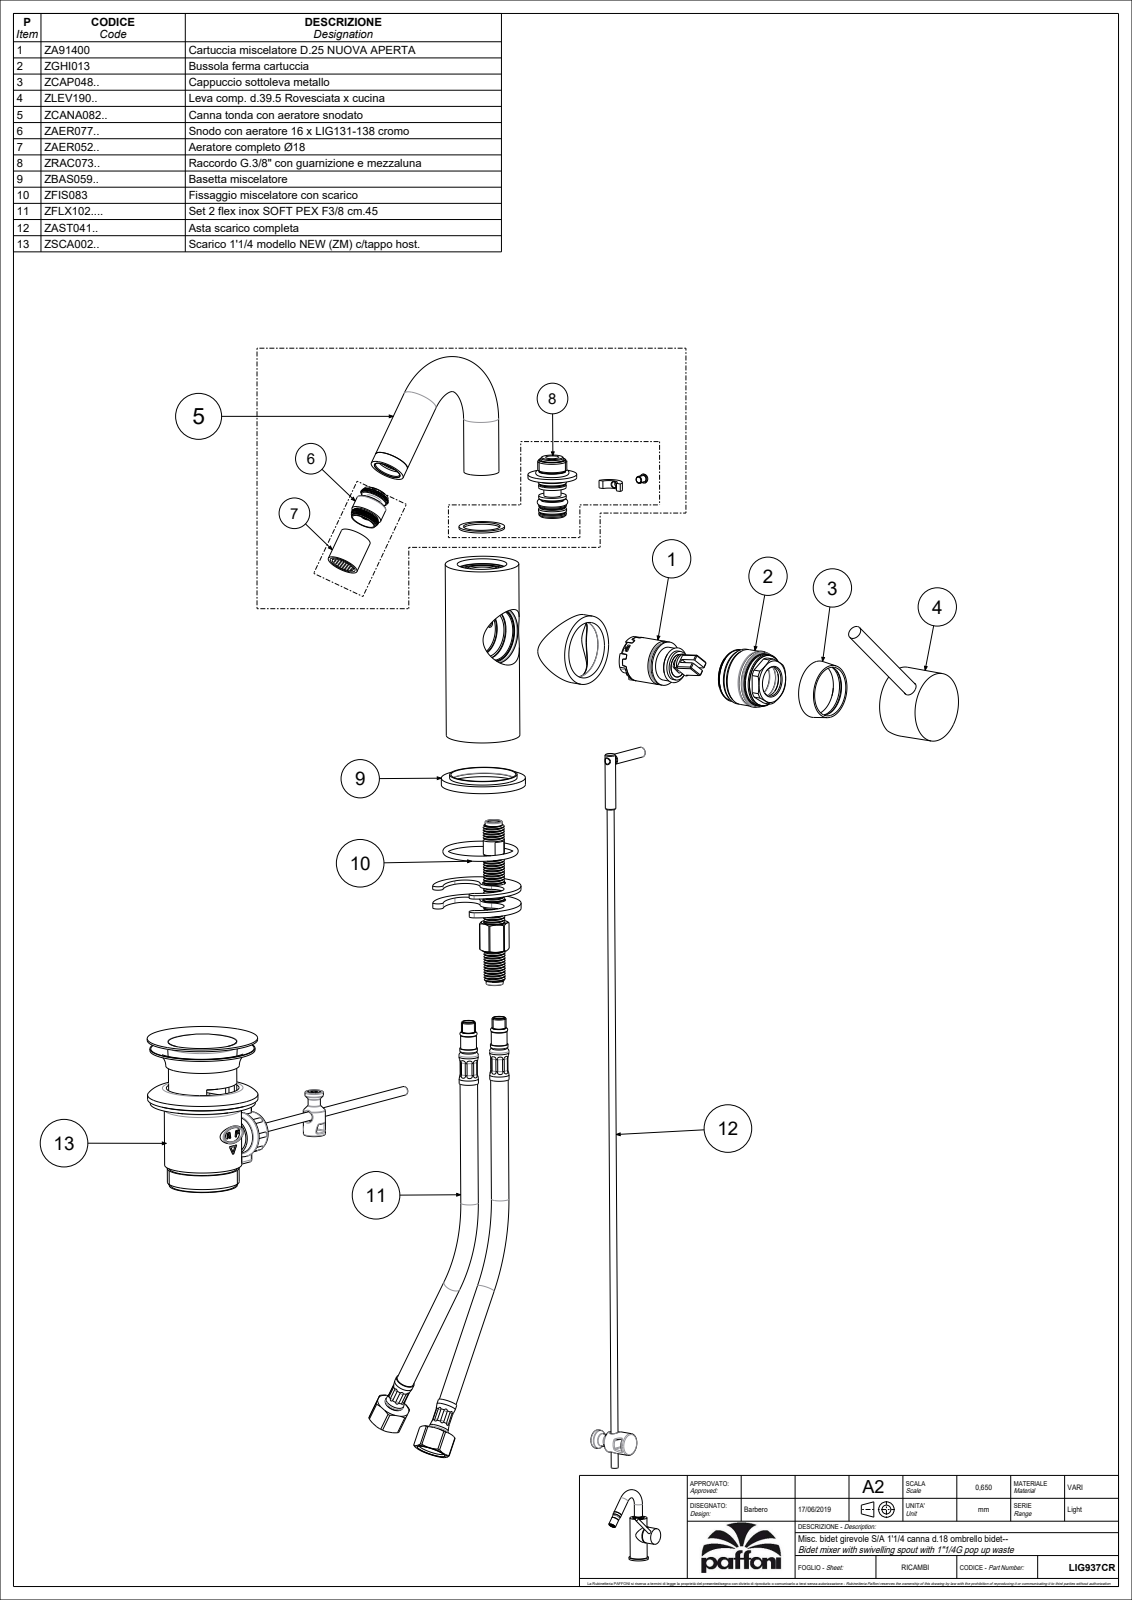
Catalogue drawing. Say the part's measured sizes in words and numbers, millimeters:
The part is named "LIG937CR". Its 3-D file was written by "CREO PARAMETRIC BY PTC INC, 2020044 (CONFIG_CONTROL_DESIGN)". It is 0 solids with 128 faces: 53 planar, 54 cylindrical and 21 other. Overall it measures 175.5 by 143.16 by 79.15 millimeters. Round holes: 1 of diameter 3. Round bosses or shafts: 3 of diameter 20, 1 of diameter 48, 1 of diameter 42, 1 of diameter 39.5, 1 of diameter 18, 1 of diameter 10, 1 of diameter 7.9, 1 of diameter 7.6. Partial cylindrical surfaces (rounded edges, fillets, slot ends): 8 of radius 1, 2 of radius 0.8, 1 of radius 3.5, 1 of radius 5, 1 of radius 6.4. The main face-to-face distances are 4, 104, 100, 10, 25.15, 15.15, 7.5, 1.5, 6, 0.5.
